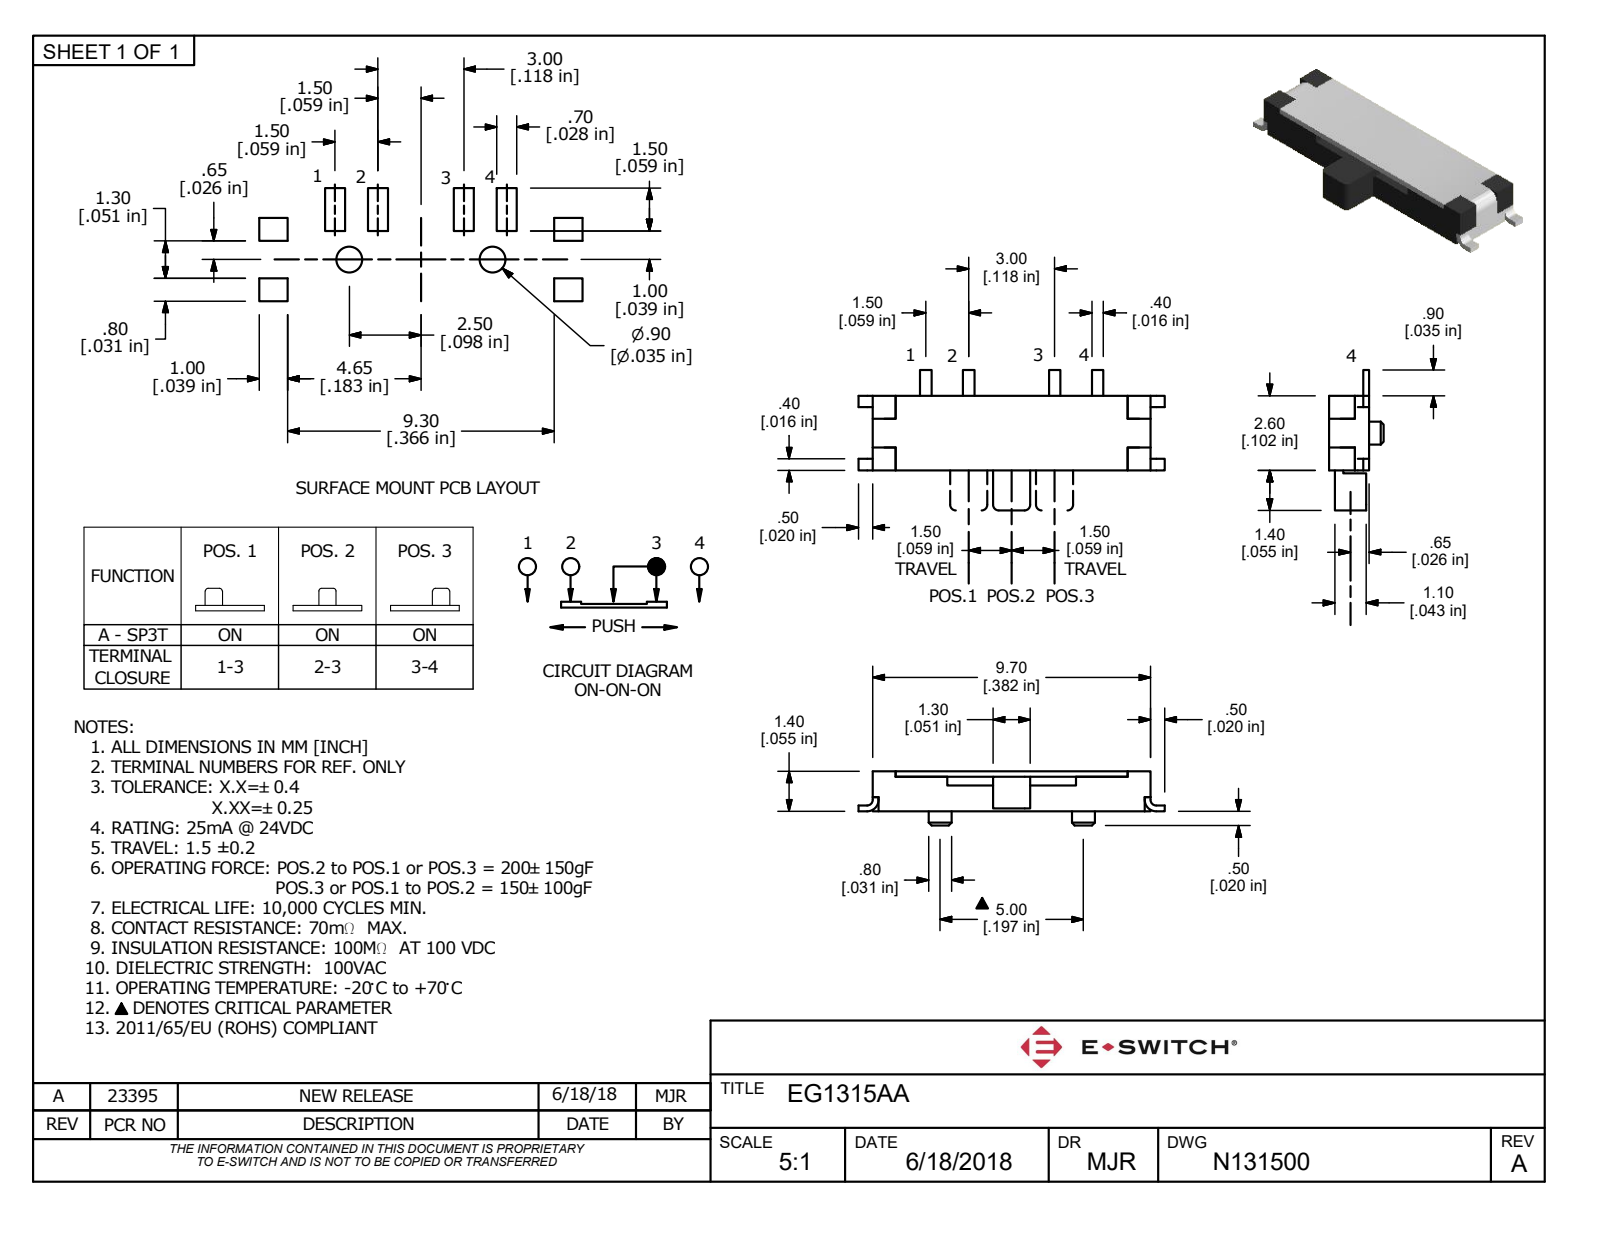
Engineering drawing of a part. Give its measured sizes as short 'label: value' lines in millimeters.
name: EG1315AA
written by: Autodesk Inventor 2018 (AUTOMOTIVE_DESIGN)
unit: mm
bodies: 1 solid, 119 faces (99 planar, 18 cylindrical, 2 other)
size: 10.7 × 4.9 × 1.9
volume: 37 mm³; area: 110 mm²
bosses: 2× ⌀0.8
rounds: 5× R0.2, 4× R0.4
face distances: 1.4, 2.6, 1.2, 1.3, 0.9, 0.5, 4.2, 5.5, 9.7, 0.7
